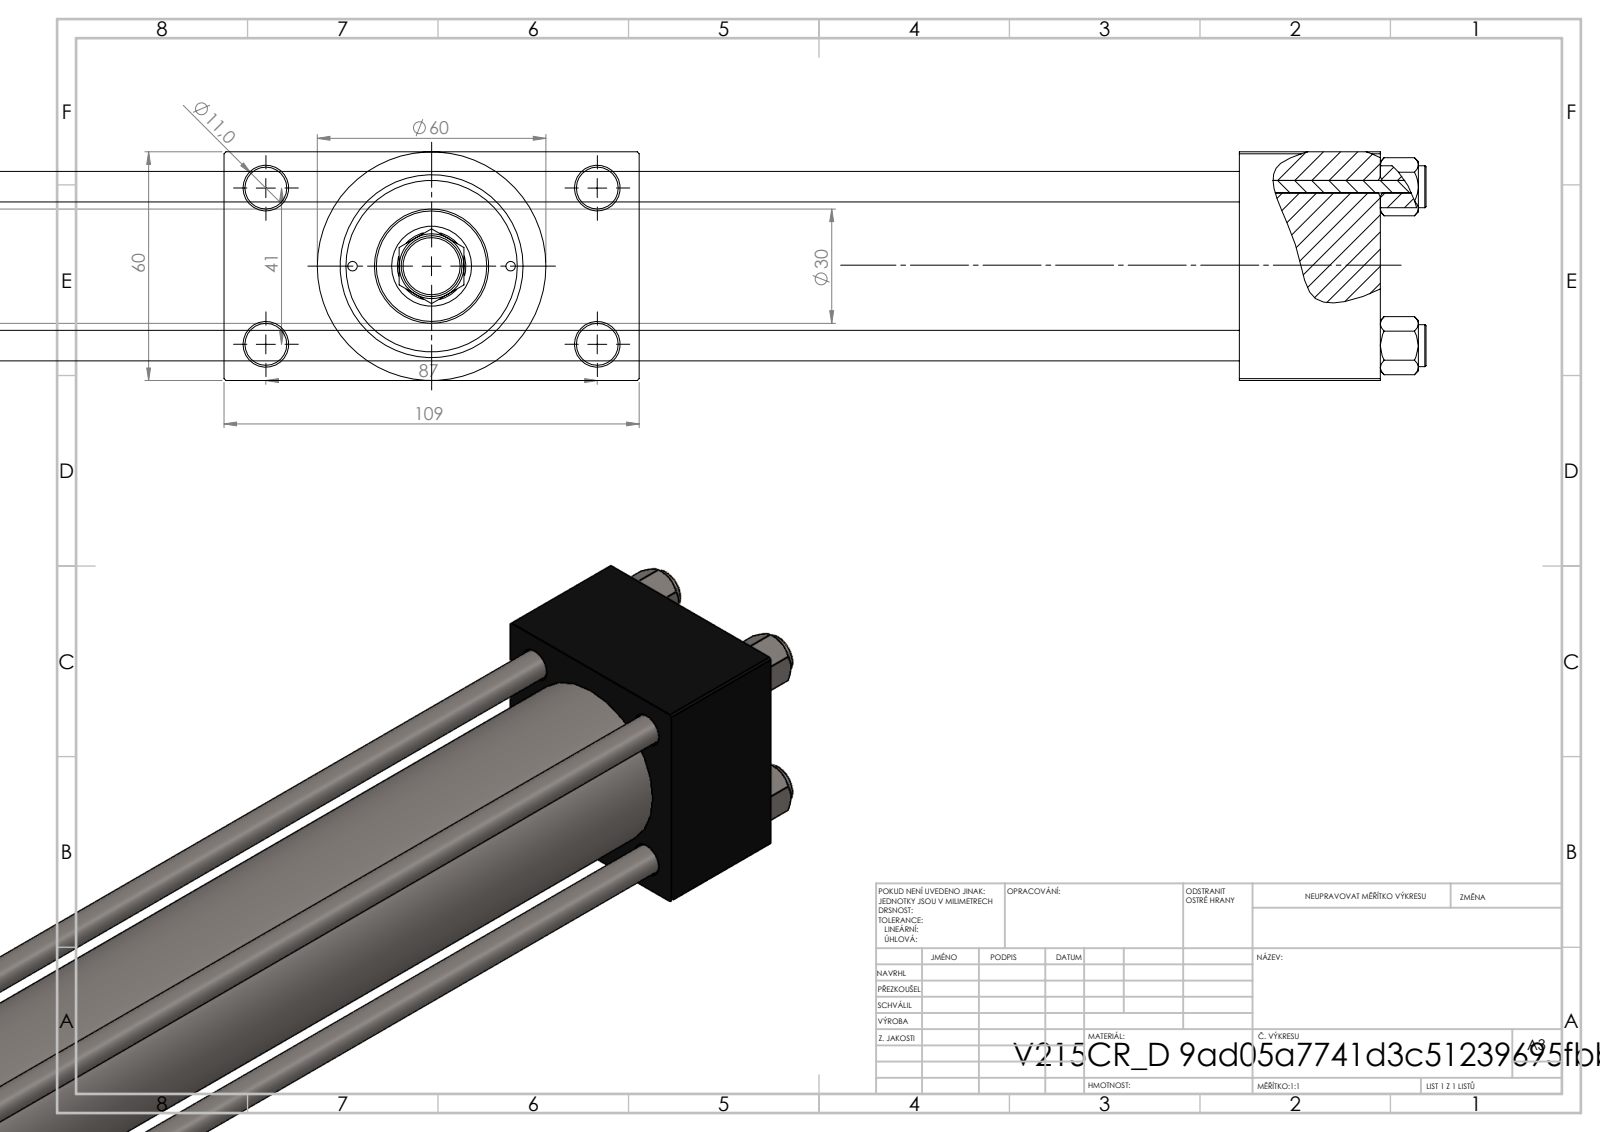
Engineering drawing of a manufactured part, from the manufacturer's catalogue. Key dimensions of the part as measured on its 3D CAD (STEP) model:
Part name (STEP PRODUCT): V215CR_D_TYCINKA; V215CR_VCP_D; MFA; NUT_M5_D (+2 more)
STEP written by: SolidWorks 2019 (CONFIG_CONTROL_DESIGN)
Units: millimetres
Bodies: 12 solids, 1164 faces (516 planar, 96 cylindrical, 552 other)
Overall size (bounding box): 593 × 109 × 60
Volume: 844 839 mm³ · Surface area: 286 926 mm²
Round holes (diameter × count): ⌀8 ×4, ⌀11 ×4, ⌀2.5 ×2, ⌀7 ×2, ⌀16.66 ×2, ⌀24 ×2, ⌀8.5 ×1, ⌀18 ×1, ⌀21 ×1, ⌀31 ×1, ⌀40 ×1, ⌀45 ×1
Round bosses / shafts (diameter × count): ⌀11 ×4, ⌀60 ×1, ⌀46 ×1, ⌀30 ×1, ⌀16 ×1, ⌀10 ×1
Partial cylindrical surfaces — rounded edges, fillets, slot ends (radius × count): R8.5 ×1
Main face-to-face distances: 60, 438, 24.5, 84.5, 37, 475, 518, 481, 43, 484.74
Hole centre spacings: 20.85, 22.65, 29.49, 30.62, 41.7, 46.53, 47.15, 48.09
